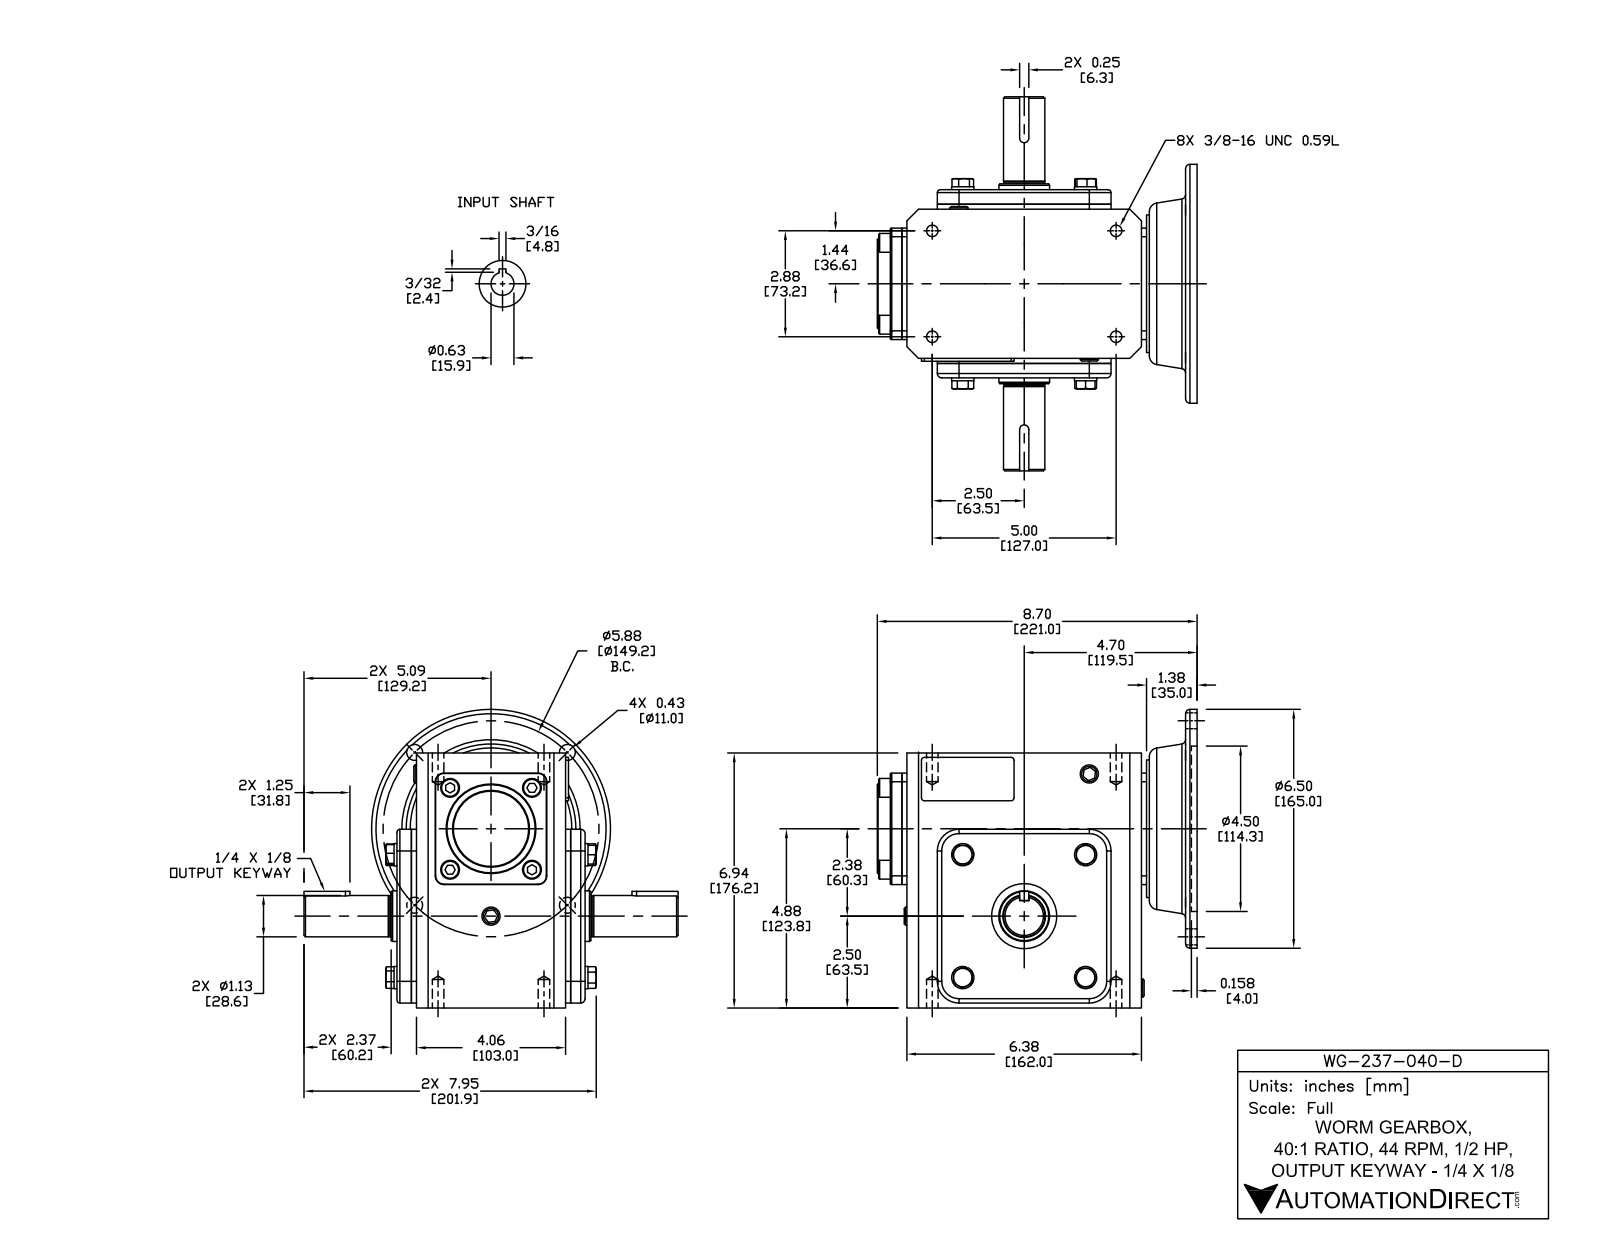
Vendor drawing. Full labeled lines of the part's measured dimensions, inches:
Part name (STEP PRODUCT): WG-237-040-D
STEP written by: SolidWorks 2015 (CONFIG_CONTROL_DESIGN)
Units: inches
Bodies: 39 solids, 572 faces (308 planar, 164 cylindrical, 100 other)
Overall size (bounding box): 10.173 × 8.701 × 8.123
Volume: 226.1 in³ · Surface area: 525.6 in²
Round holes (diameter × count): ⌀0.313 ×4, ⌀0.406 ×4, ⌀0.591 ×1, ⌀0.625 ×1, ⌀1.378 ×1, ⌀1.457 ×1, ⌀1.772 ×1, ⌀3.819 ×1, ⌀4.5 ×1
Round bosses / shafts (diameter × count): ⌀0.606 ×4, ⌀0.512 ×4, ⌀6.496 ×1, ⌀3.74 ×1, ⌀2.441 ×1, ⌀2.047 ×1, ⌀1.181 ×1, ⌀1.142 ×1
Partial cylindrical surfaces — rounded edges, fillets, slot ends (radius × count): R0.079 ×8, R0.118 ×8, R0.236 ×6, R0.591 ×4, R0.02 ×2, R0.039 ×2, R0.125 ×2
Main face-to-face distances: 0.138, 4.331, 4.724, 0.394, 0.531, 4.587, 4.193, 6.516, 6.937, 0.315
Hole centre spacings: 2.937, 2.098, 2.88, 4.154, 4.154, 4.913, 5, 5.77
